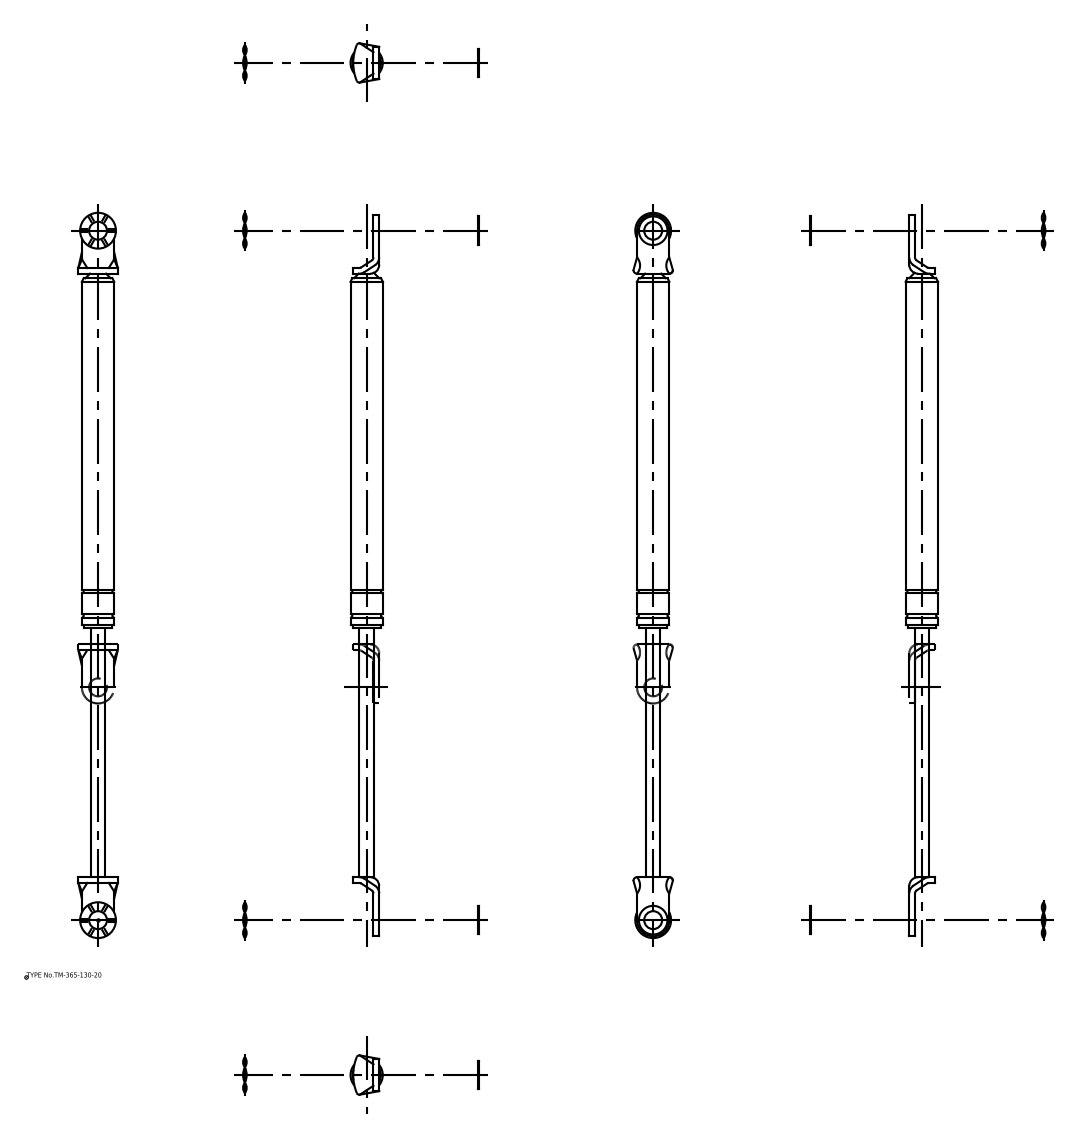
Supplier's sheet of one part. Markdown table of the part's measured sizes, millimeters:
| quantity | value |
| --- | --- |
| part name | ウェーブワッシャー; ワッシャー; 本体; 本体_div |
| STEP written by | spGate 16.7.1 (AUTOMOTIVE_DESIGN) |
| units | millimeters |
| bodies | 6 solids, 94 faces (42 planar, 44 cylindrical, 8 other) |
| overall size | 405 × 22 × 18.5 |
| volume | 62 350 mm³ |
| surface area | 20 703 mm² |
| round holes (diameter × count) | 10 × 2 |
| round bosses / shafts (diameter × count) | 16 × 3, 20 × 2, 18.5 × 1, 18 × 1, 8 × 1 |
| partial cylindrical surfaces (radius × count) | 4.4 × 2, 5 × 2, 9 × 2, 26.32 × 1 |
| main face-to-face distances | 3.2, 2, 5.2, 340.2, 3.7, 5.7, 0.5, 201.2, 142.2, 343.4 |
| hole center spacings | 385 |
